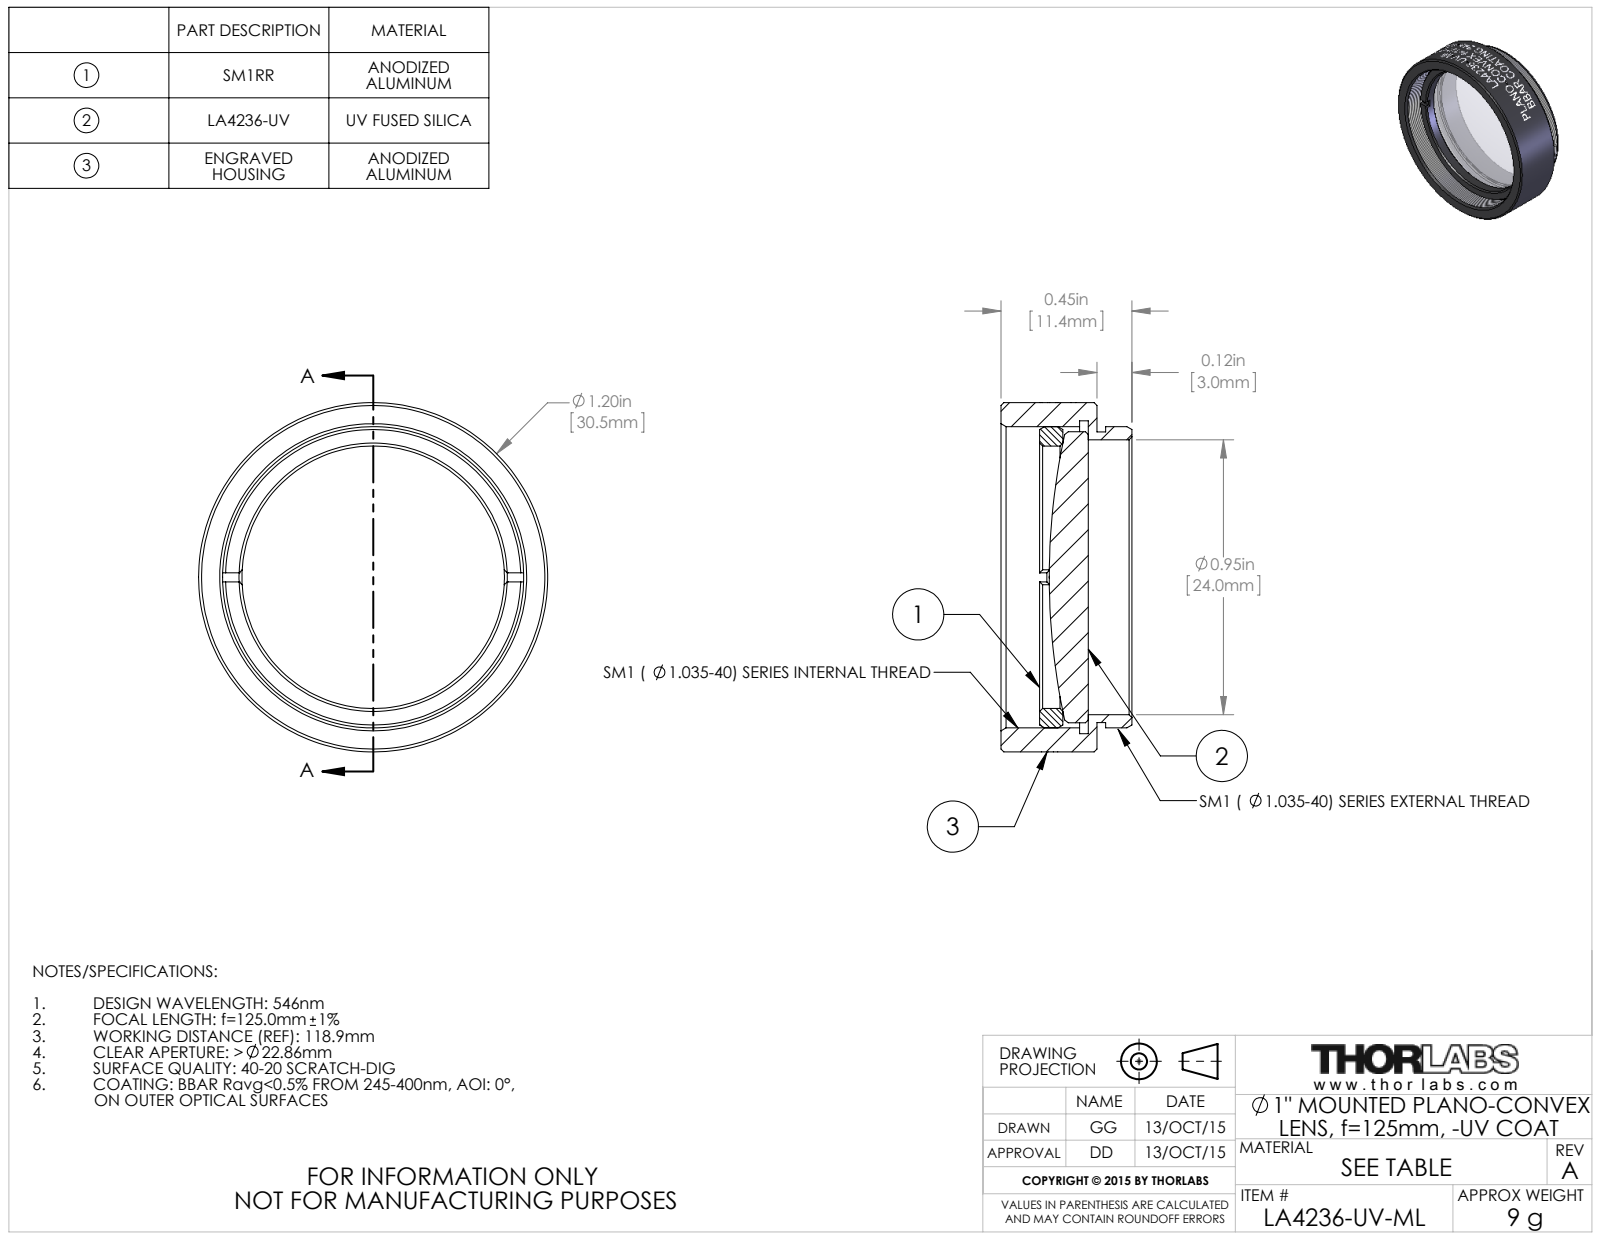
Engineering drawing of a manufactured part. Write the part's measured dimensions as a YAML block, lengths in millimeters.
part_name: "TTN039218-E0W"
step_written_by: "SolidWorks 2014 (CONFIG_CONTROL_DESIGN)"
units: millimeters
bodies: {solids: 3, faces: 159, planar: 20, cylindrical: 111, other: 28}
overall_size: [30.48, 30.48, 11.43]
volume: 3448
surface_area: 4298
round_holes:
  - {diameter: 22.91, count: 1}
  - {diameter: 24, count: 1}
  - {diameter: 27.31, count: 1}
round_bosses_or_shafts:
  - {diameter: 30.48, count: 1}
  - {diameter: 26.29, count: 1}
  - {diameter: 25.4, count: 1}
  - {diameter: 25.37, count: 1}
face_to_face_distances: [0.76, 8.38, 7.62, 2.98, 2.22, 5.4, 5.01, 4.25, 2.03, 3.37]
